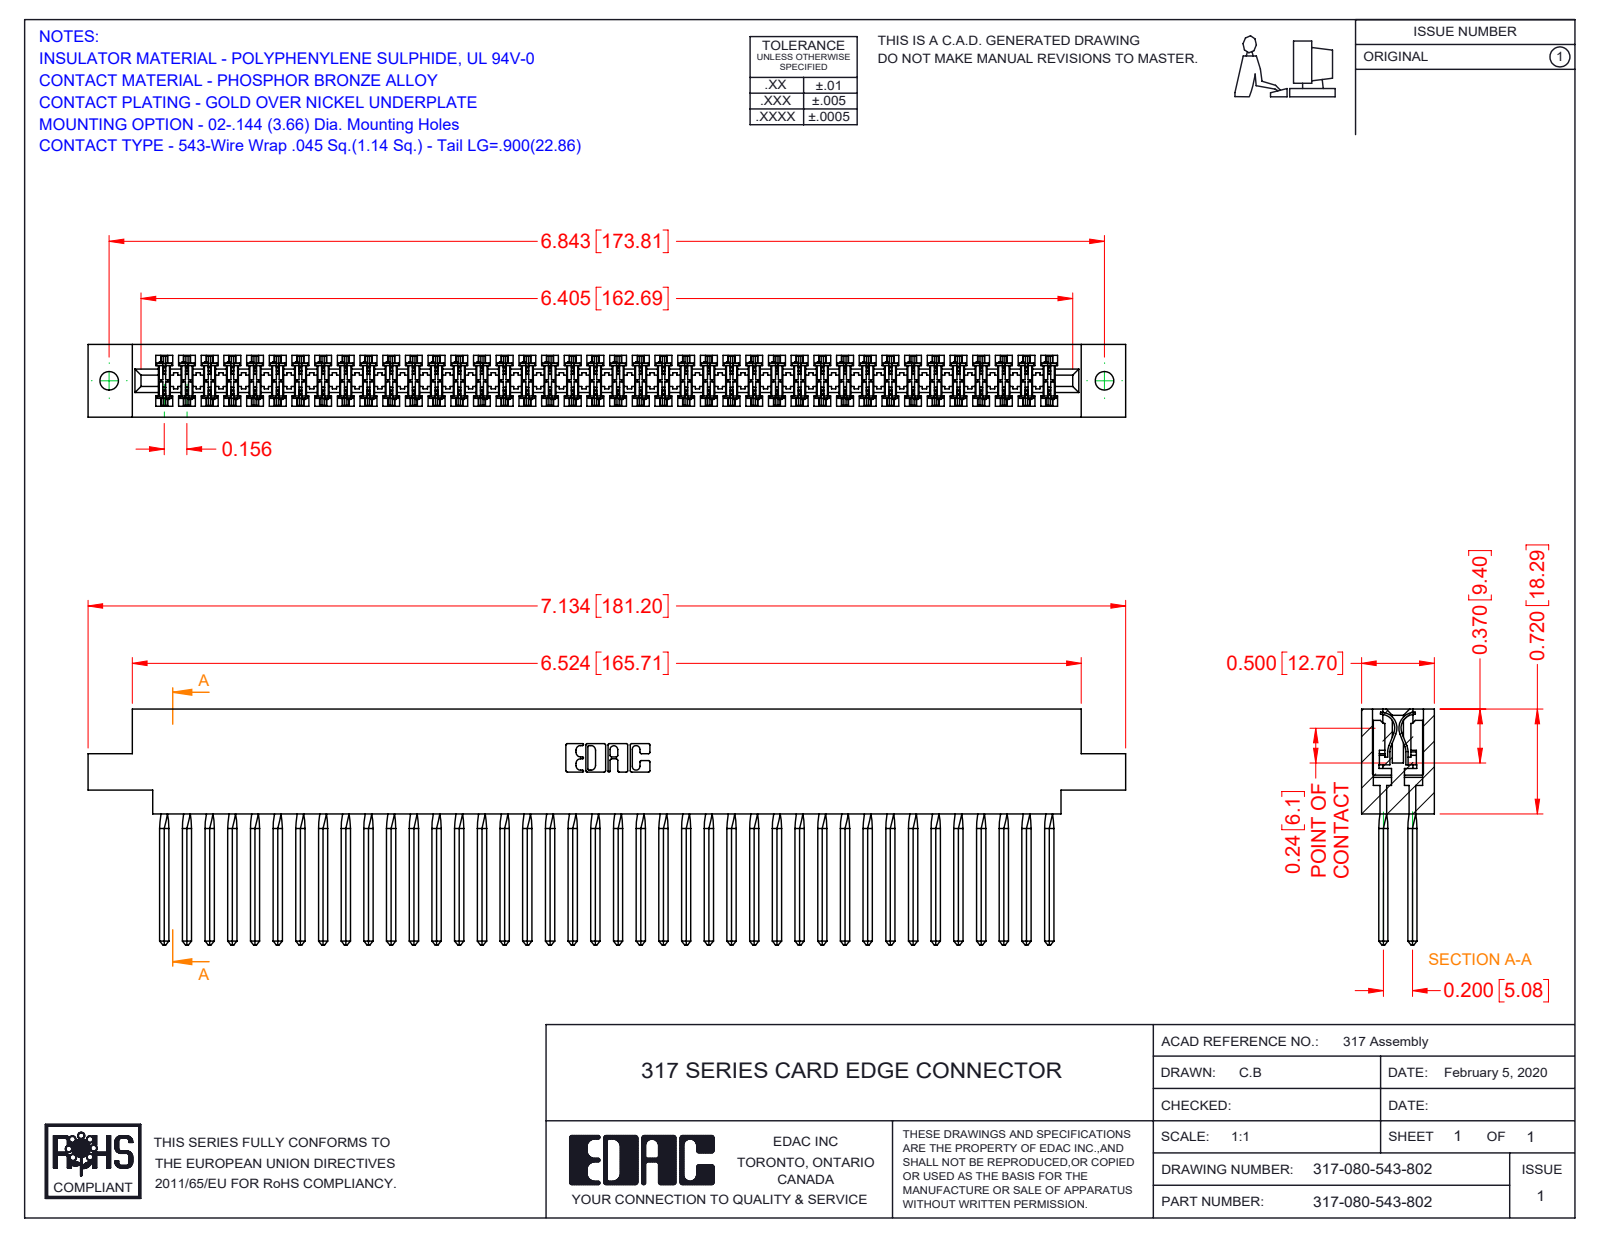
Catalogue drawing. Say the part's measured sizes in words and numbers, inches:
The part is named "317 Part_.144 Dia; 317-080-543-802; 317-290-001_543". Its 3-D file was written by "SolidWorks 2016 (CONFIG_CONTROL_DESIGN)". It is 81 solids with 7222 faces: 5898 planar, 1004 cylindrical and 320 other. Overall it measures 7.134 by 1.62 by 0.5 inches. Its volume is 1.874 cubic inches and its surface area 71.67 square inches. Round holes: 2 of diameter 0.128. Partial cylindrical surfaces (rounded edges, fillets, slot ends): 160 of radius 0.015, 22 of radius 0.01, 6 of radius 0.007, 6 of radius 0.031, 3 of radius 0.026, 2 of radius 0.095, 2 of radius 0.1, 2 of radius 0.11. The main face-to-face distances are 0.5, 0.075, 0.425, 0.35, 0.11, 0.195, 0.094, 0.2, 0.115, 0.131. The hole center spacings are 6.843.
